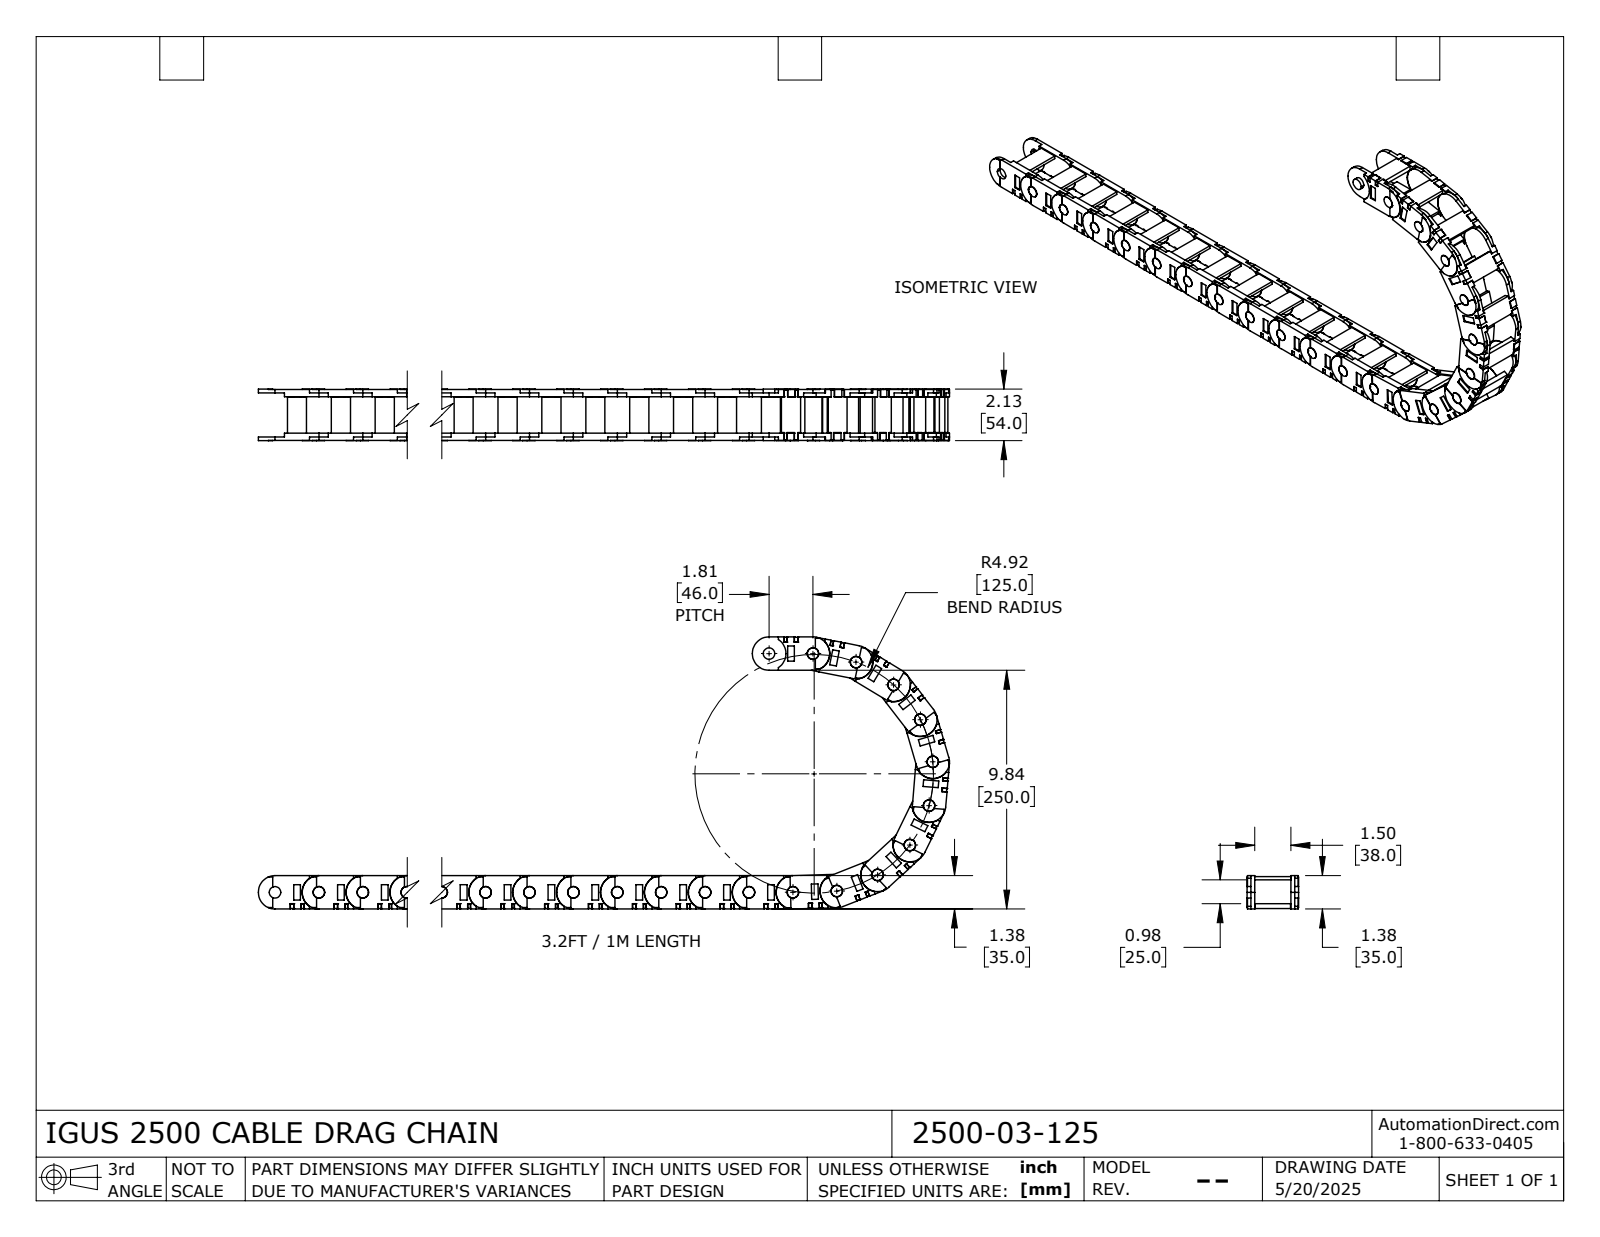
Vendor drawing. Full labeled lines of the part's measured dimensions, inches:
Part name (STEP PRODUCT): 2500_03_125
STEP written by: SolidWorks 2024 (AUTOMOTIVE_DESIGN)
Units: inches
Bodies: 66 solids, 2398 faces (1870 planar, 528 cylindrical, 0 other)
Overall size (bounding box): 28.879 × 11.22 × 2.126
Volume: 40.89 in³ · Surface area: 601.2 in²
Round holes (diameter × count): ⌀0.473 ×22
Round bosses / shafts (diameter × count): ⌀0.472 ×22, ⌀1.378 ×21
Partial cylindrical surfaces — rounded edges, fillets, slot ends (radius × count): R0.697 ×23, R0.689 ×2
Main face-to-face distances: 0.157, 1.654, 1.811, 0.142, 0.299, 1.795, 1.953, 1.496, 0.016, 2.094
Hole centre spacings: 1.811, 3.622, 5.433, 7.244, 9.055, 10.866, 12.677, 3.56
